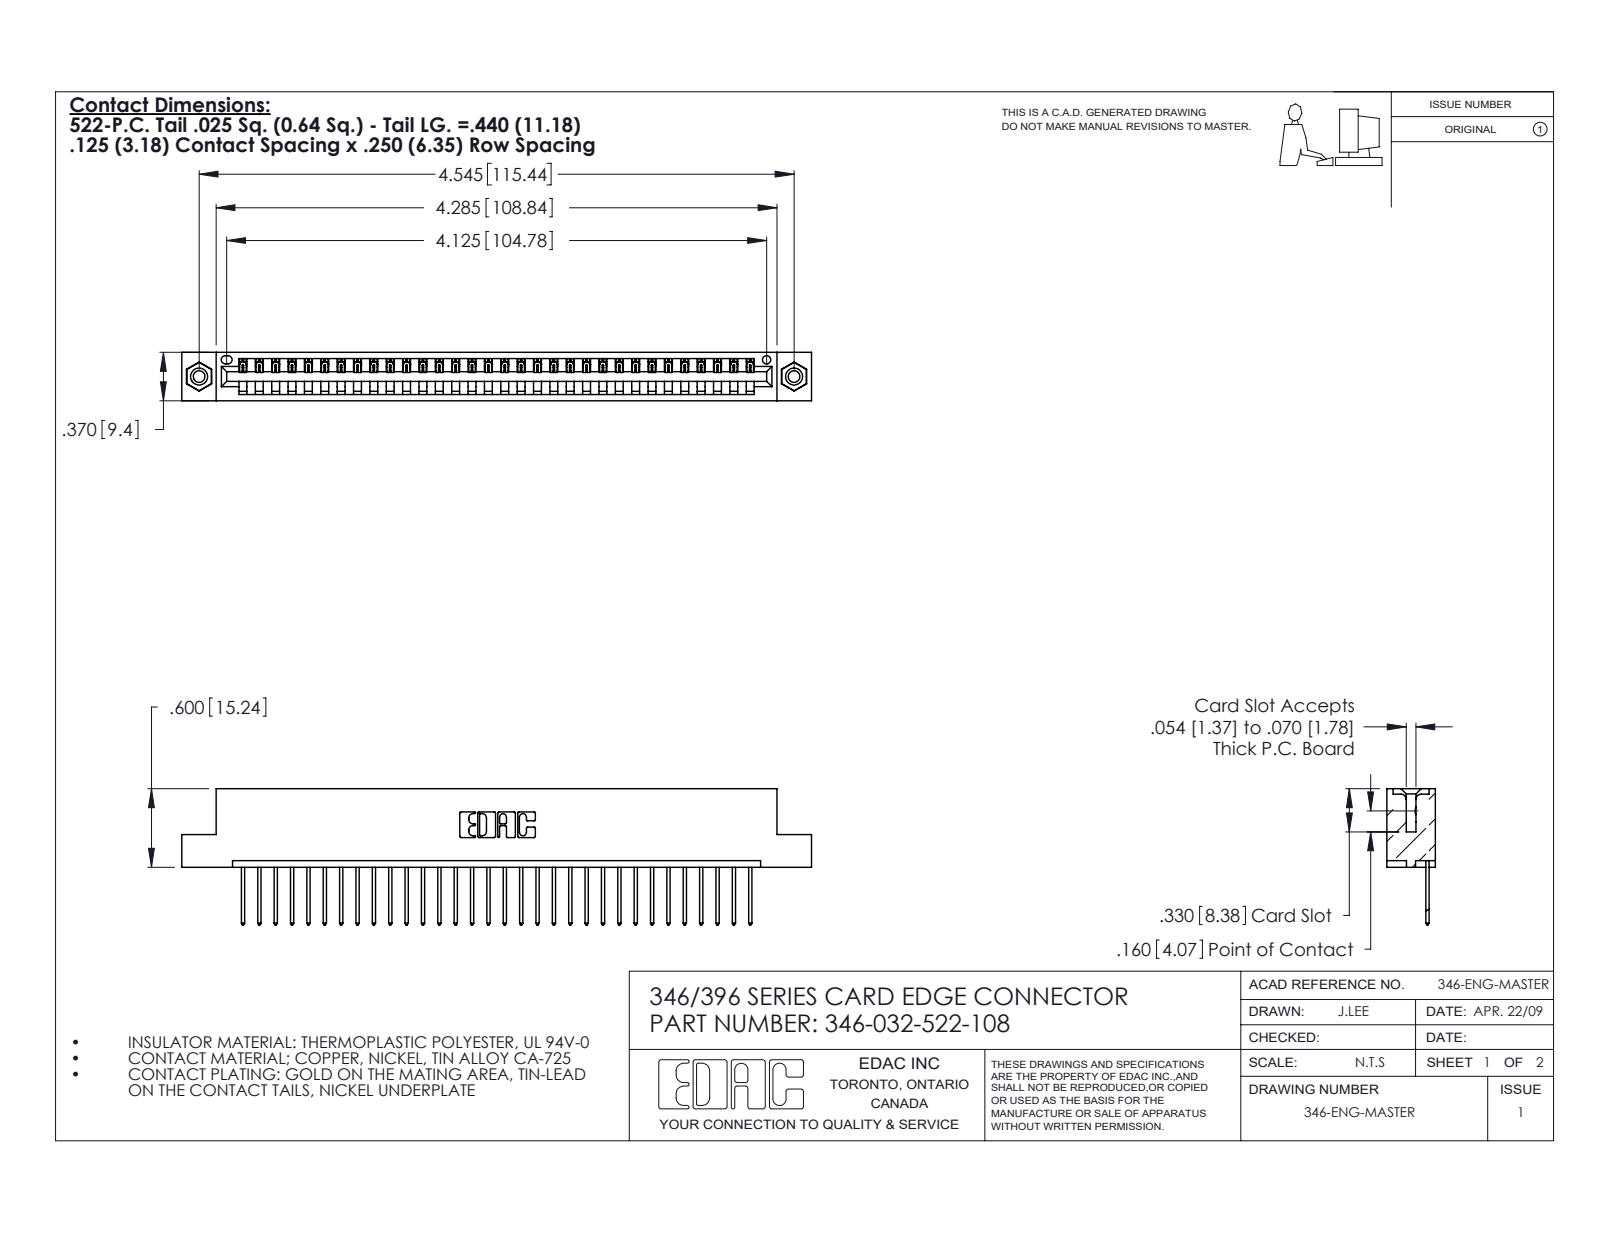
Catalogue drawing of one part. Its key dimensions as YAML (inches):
part_name: "345-292-001_345-293-122; 345-250-001_345-250-003-102; 346-032-522-108; 346 Part_Flush Mounting Lugs - 0.156 Dia-TI"
step_written_by: "SolidWorks 2020 (CONFIG_CONTROL_DESIGN)"
units: inches
bodies: {solids: 35, faces: 2038, planar: 1388, cylindrical: 634, other: 16}
overall_size: [4.81, 1.04, 0.37]
volume: 0.709
surface_area: 22.57
round_holes:
  - {diameter: 0.089, count: 2}
  - {diameter: 0.125, count: 2}
  - {diameter: 0.156, count: 2}
  - {diameter: 0.064, count: 1}
round_bosses_or_shafts:
  - {diameter: 0.155, count: 2}
partial_cylinders:
  - {radius: 0.006, count: 64}
  - {radius: 0.01, count: 64}
  - {radius: 0.01, count: 22}
  - {radius: 0.007, count: 6}
  - {radius: 0.031, count: 6}
  - {radius: 0.026, count: 3}
  - {radius: 0.031, count: 2}
  - {radius: 0.04, count: 2}
face_to_face_distances: [0.048, 0.322, 0.37, 0.25, 0.072, 0.298, 0.025, 0.148, 0.222, 0.1]
hole_center_spacings: [0.246, 4.337, 4.545]
